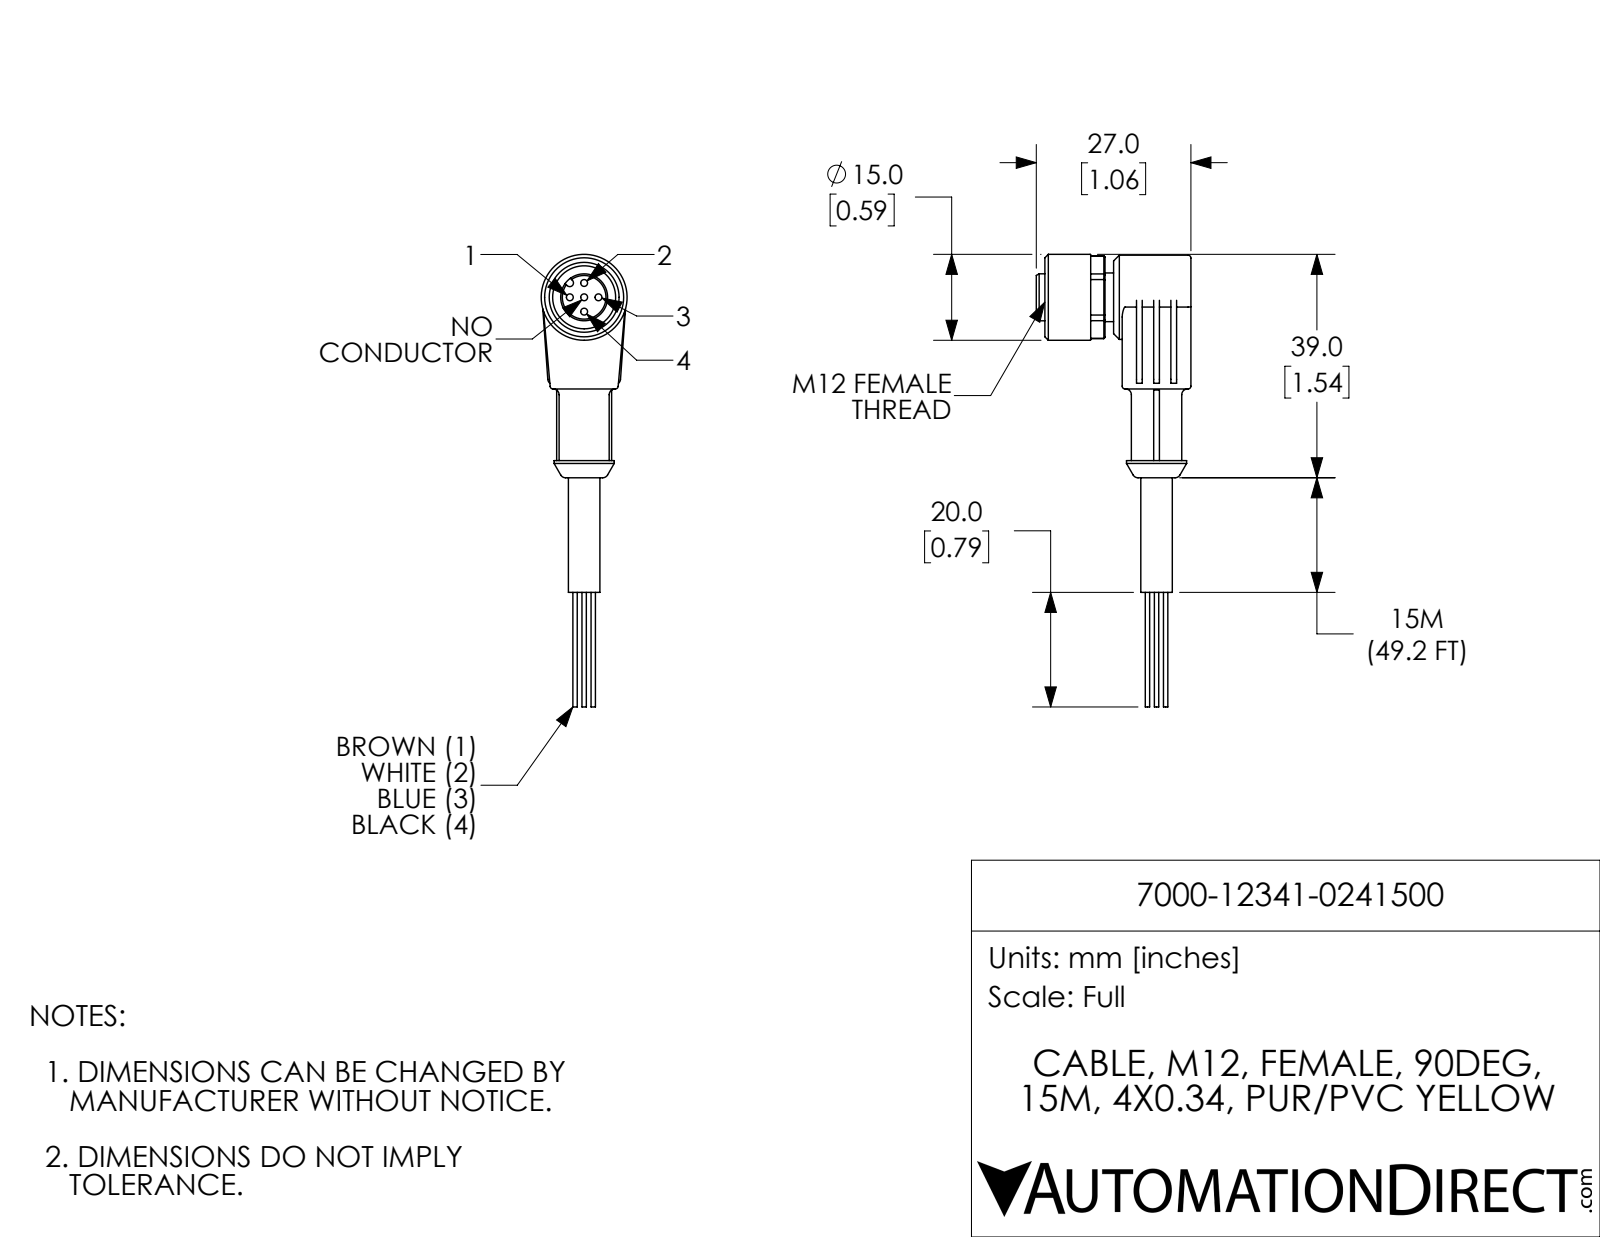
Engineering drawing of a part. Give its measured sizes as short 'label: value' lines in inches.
name: 7000-12341-0241500
written by: SolidWorks 2017 (AUTOMOTIVE_DESIGN)
unit: in
bodies: 1 solid, 152 faces (65 planar, 59 cylindrical, 28 other)
size: 3.11 × 1.063 × 0.591
volume: 0.417 in³; area: 5.896 in²
holes: 5× ⌀0.047, 1× ⌀0.189, 1× ⌀0.433
bosses: 4× ⌀0.03, 1× ⌀0.591, 1× ⌀0.579, 1× ⌀0.413, 1× ⌀0.346, 1× ⌀0.335, 1× ⌀0.323, 1× ⌀0.217
rounds: 8× R0.02, 2× R0.039, 1× R0.026, 1× R0.283
face distances: 0.472, 0.059, 0.118, 0.531, 0.591, 0.217, 0.374, 0.236, 0.315, 0.492
hole spacings: 0.098, 0.139, 0.197
